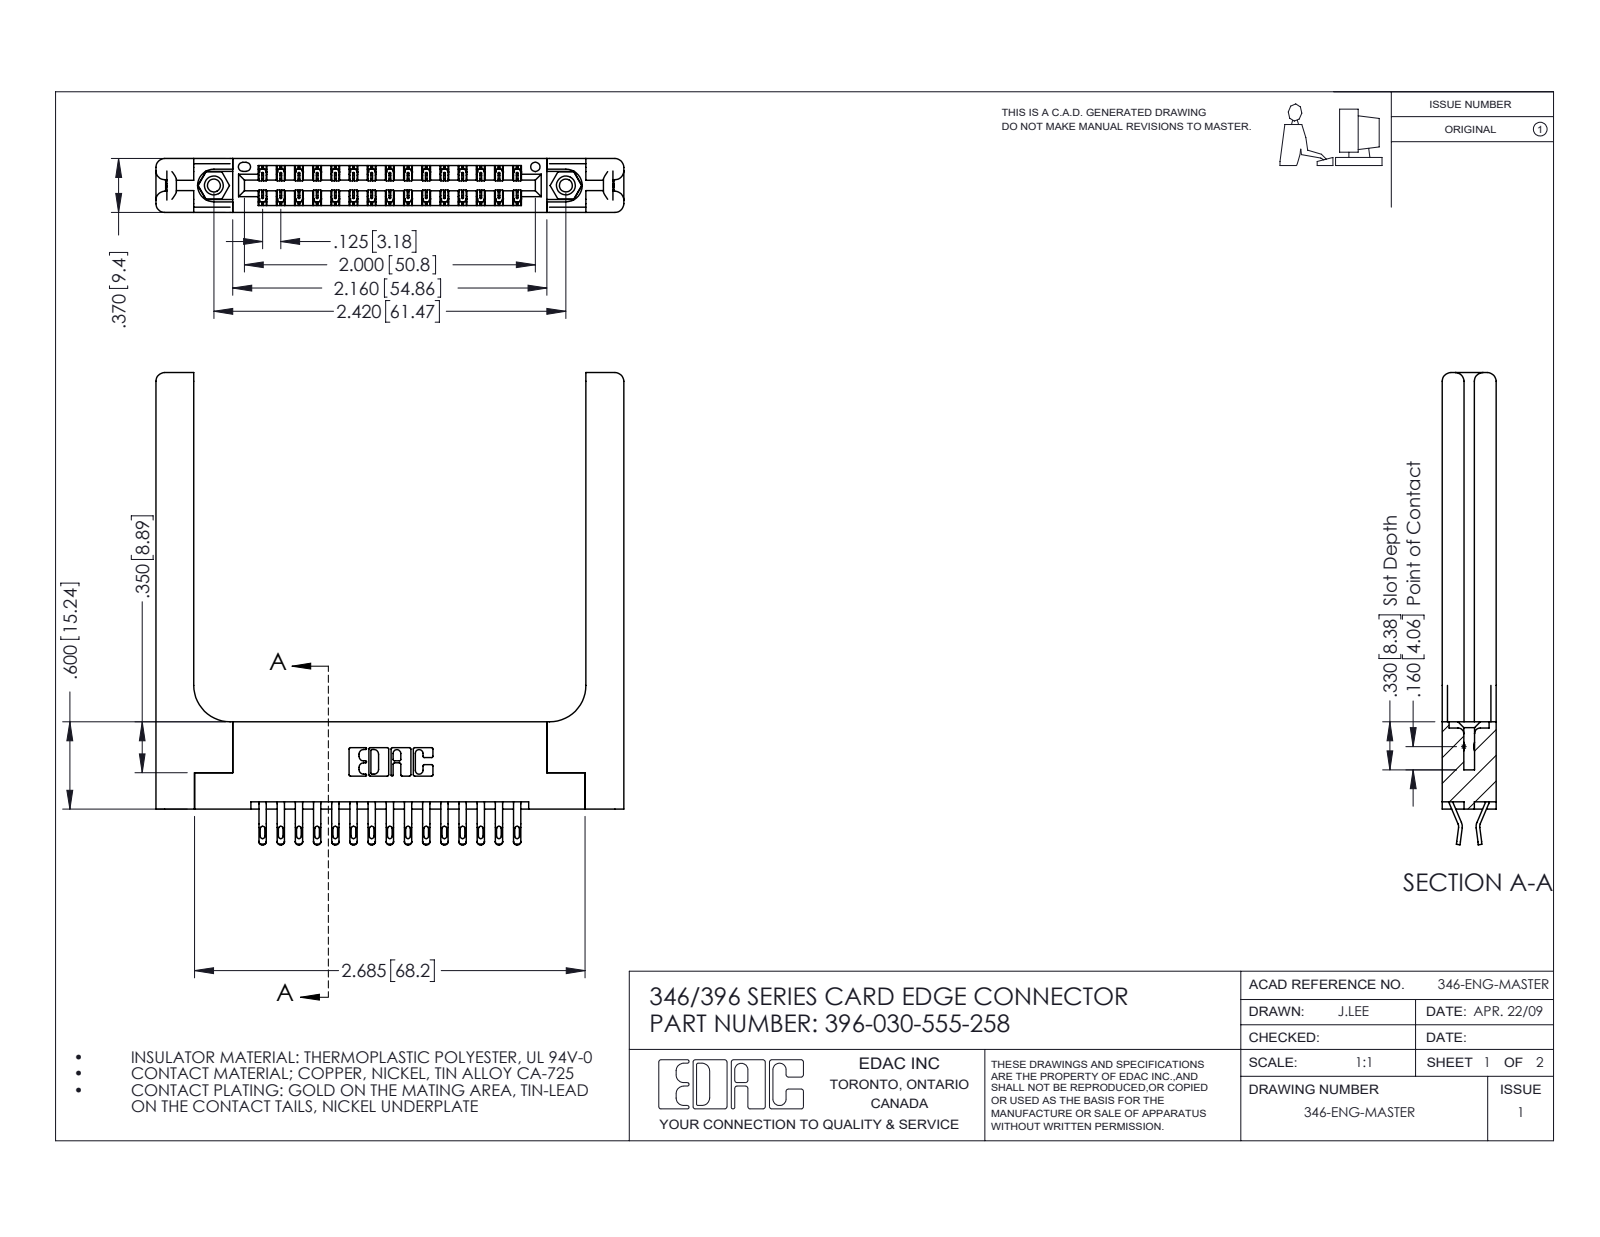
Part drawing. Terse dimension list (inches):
name: 345-250-001_345-250-001-102; 345-292-001_555 Tail; 396-030-555-258; 346-220-058_345-220-058 (+1 more)
written by: SolidWorks 2016 (CONFIG_CONTROL_DESIGN)
unit: in
bodies: 35 solids, 2118 faces (1214 planar, 844 cylindrical, 60 other)
size: 3.245 × 3.216 × 0.37
volume: 0.936 in³; area: 24.24 in²
holes: 2× ⌀0.089, 2× ⌀0.125, 2× ⌀0.156, 1× ⌀0.064
bosses: 2× ⌀0.155
rounds: 60× R0.016, 60× R0.02, 45× R0.006, 22× R0.01, 16× R0.06, 6× R0.007, 6× R0.031, 3× R0.026
face distances: 0.37, 0.15, 0.072, 0.148, 0.048, 0.322, 0.25, 0.102, 0.22, 0.173
hole spacings: 0.246, 2.213, 2.42
